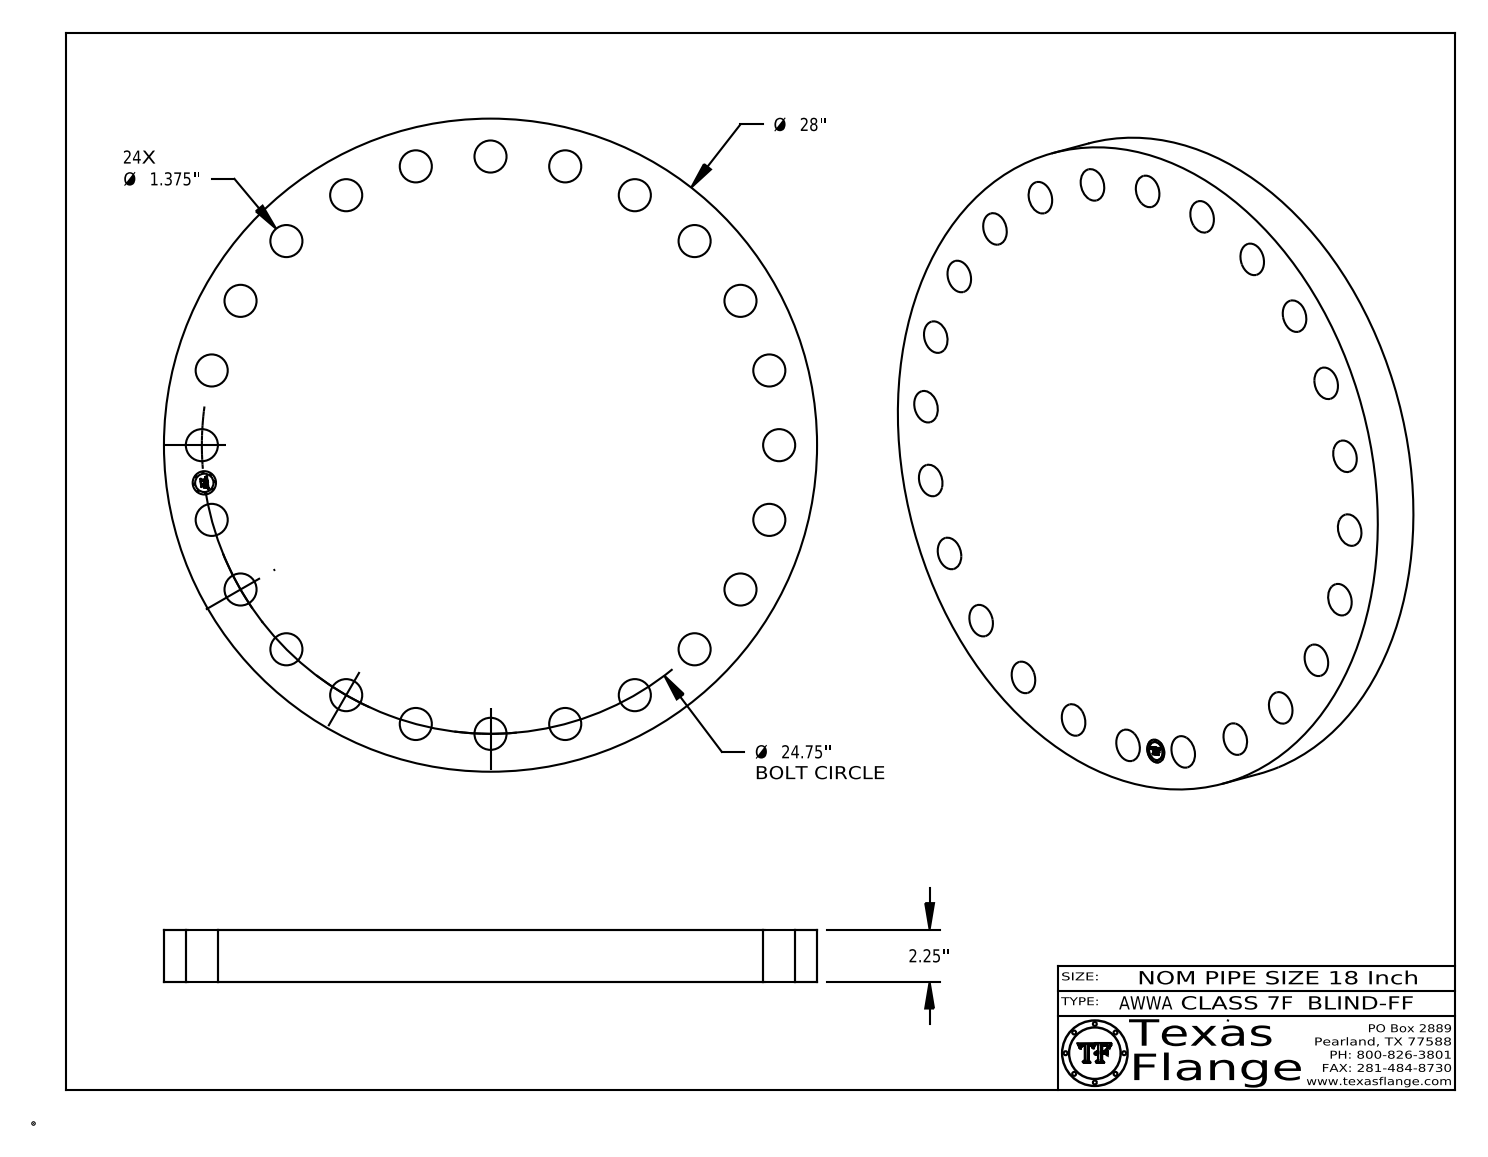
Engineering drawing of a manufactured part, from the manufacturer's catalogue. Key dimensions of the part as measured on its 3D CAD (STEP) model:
Part name (STEP PRODUCT): AWWA Class 7F-BLIND-FF
STEP written by: CATIA V5 STEP AP214 (AUTOMOTIVE_DESIGN)
Units: inches
Bodies: 1 solid, 437 faces (367 planar, 70 cylindrical, 0 other)
Overall size (bounding box): 28 × 28 × 2.25
Volume: 1 305 in³ · Surface area: 1 592 in²
Round holes (diameter × count): ⌀1.375 ×24, ⌀1 ×1
Round bosses / shafts (diameter × count): ⌀0.061 ×8, ⌀28 ×1, ⌀0.788 ×1
Main face-to-face distances: 2.25, 0.015, 2.235, 0.298, 0.292, 0.055, 0.193, 0.248, 0.044, 0.15
Hole centre spacings: 9.471, 12.375, 15.067, 17.501, 21.434, 22.866, 23.906, 3.23
